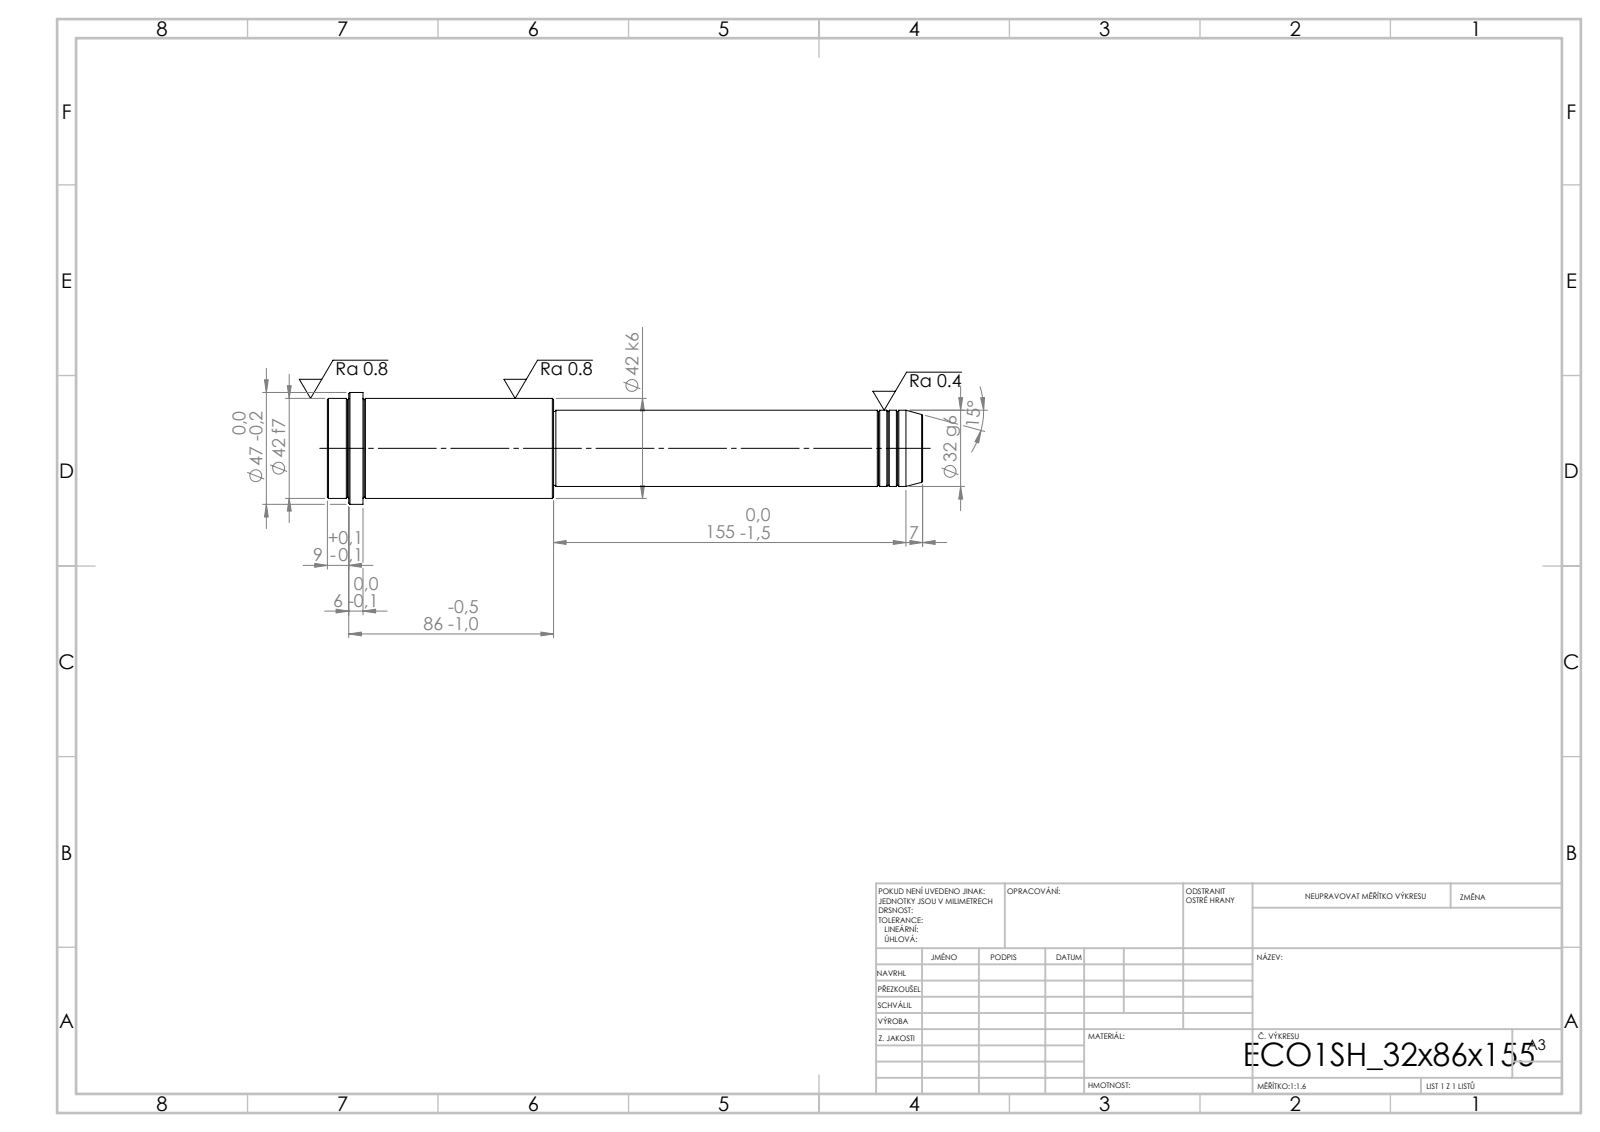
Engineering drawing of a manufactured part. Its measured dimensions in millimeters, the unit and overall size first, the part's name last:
Units: millimetres
Overall size (bounding box): 250 × 47 × 47
Round bosses / shafts (diameter × count): ⌀47 ×1, ⌀42 ×1, ⌀32 ×1, ⌀31 ×1
Main face-to-face distances: 250, 155, 95, 235, 80, 15, 241, 86, 6, 9
Volume: 257 416 mm³ · Surface area: 31 757 mm²
Bodies: 1 solid, 52 faces (6 planar, 16 cylindrical, 30 other)
STEP written by: SolidWorks 2019 (CONFIG_CONTROL_DESIGN)
